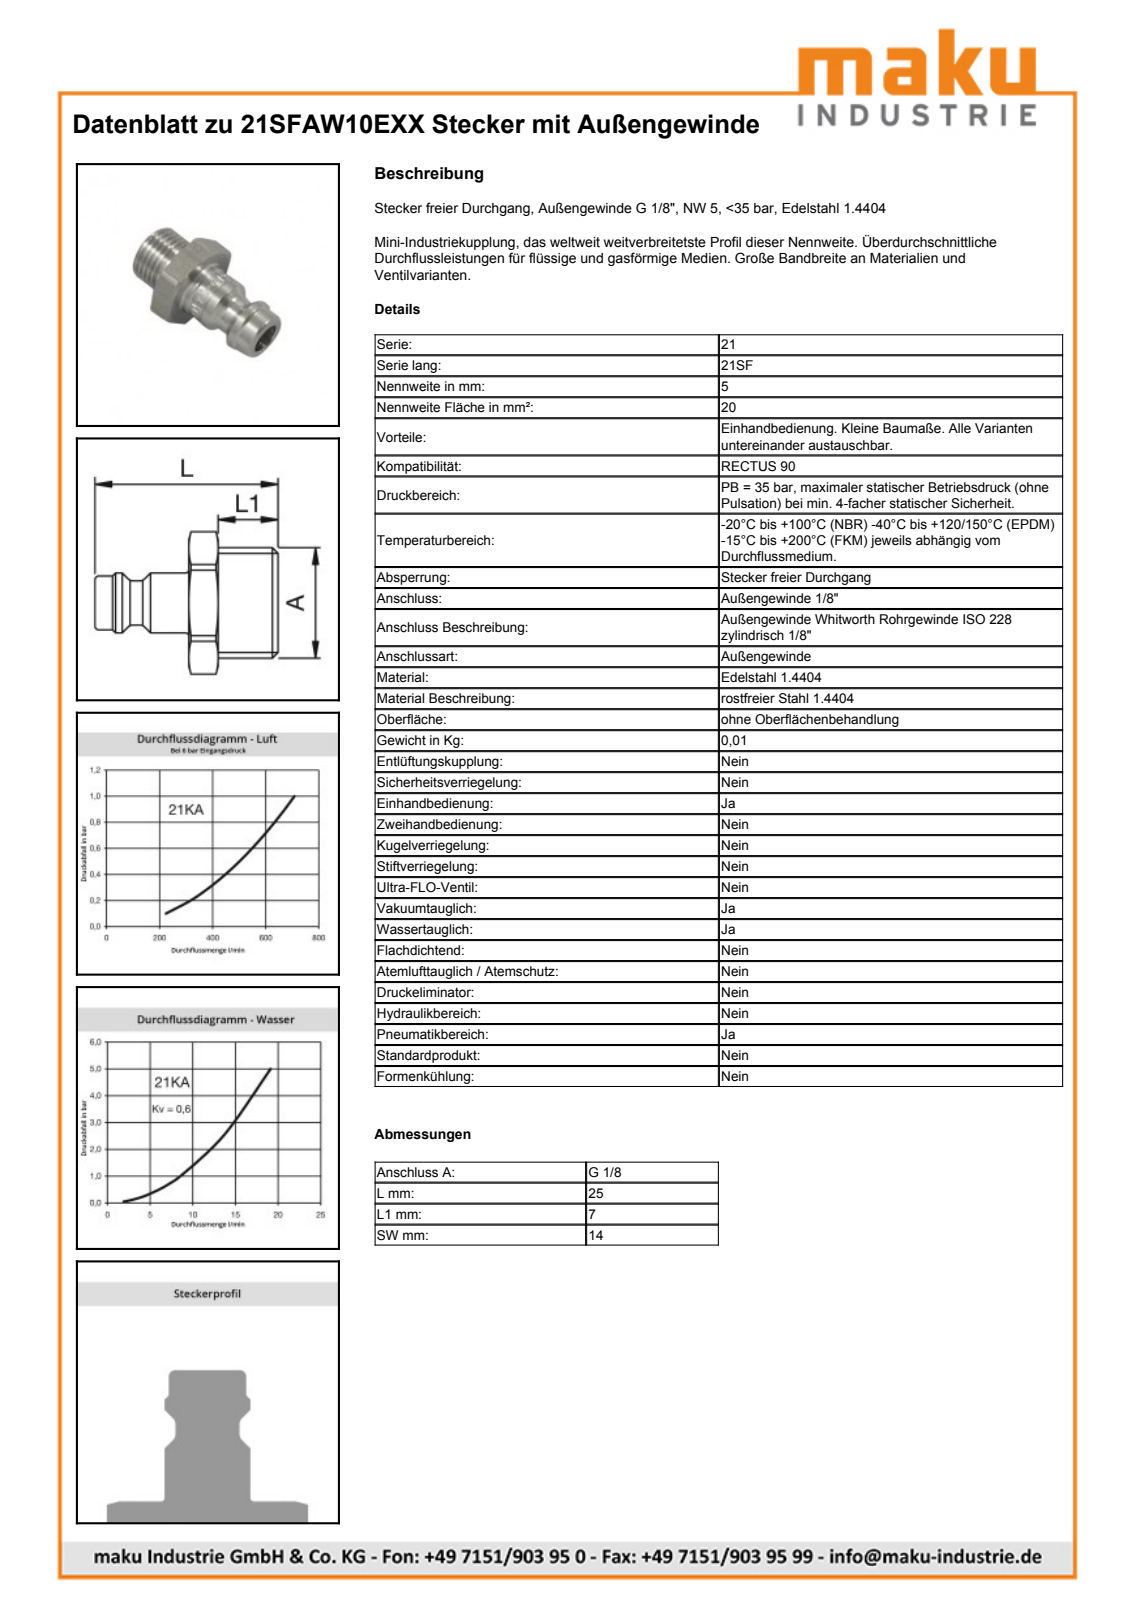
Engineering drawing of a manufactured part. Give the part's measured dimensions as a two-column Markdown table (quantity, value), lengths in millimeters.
| quantity | value |
| --- | --- |
| part name | D108932 |
| STEP written by | Autodesk Inventor 2013 (AUTOMOTIVE_DESIGN) |
| units | millimeters |
| bodies | 1 solid, 45 faces (10 planar, 12 cylindrical, 23 other) |
| overall size | 25 × 15.8 × 14 |
| volume | 1 391 mm³ |
| surface area | 1 442 mm² |
| round holes (diameter × count) | 4.95 × 1 |
| round bosses / shafts (diameter × count) | 9.73 × 1, 9 × 1, 8.1 × 1, 6.65 × 1 |
| partial cylindrical surfaces (radius × count) | 7.9 × 1 |
| main face-to-face distances | 14, 3.9, 14.1, 18, 25, 10.9, 7 |
